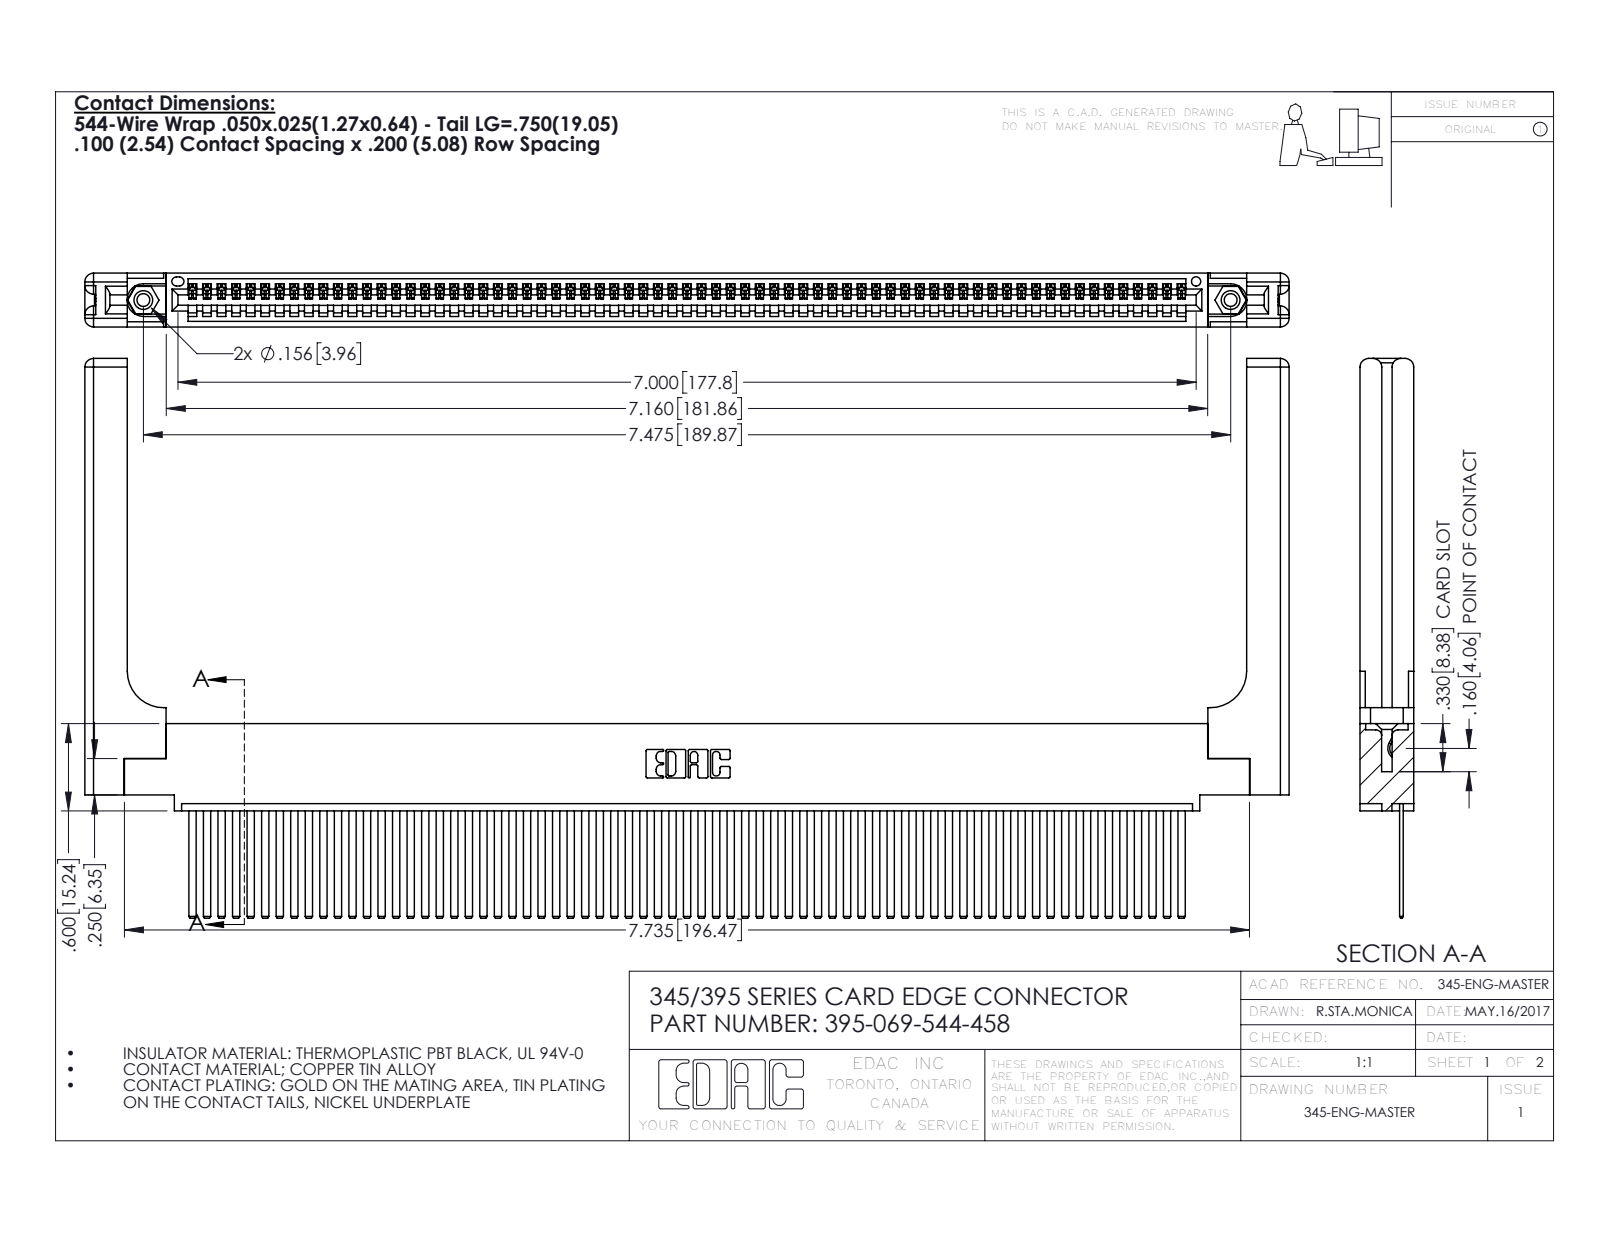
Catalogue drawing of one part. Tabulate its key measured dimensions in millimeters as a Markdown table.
| quantity | value |
| --- | --- |
| part name | 345-220-058_345-220-058; 395-069-544-458; 345-250-001_345-250-001-102; 345-292-001_345-293-144 (+1 more) |
| STEP written by | SolidWorks 2016 (CONFIG_CONTROL_DESIGN) |
| units | millimeters |
| bodies | 74 solids, 3974 faces (2716 planar, 1198 cylindrical, 60 other) |
| overall size | 210.3 × 97.7 × 9.4 |
| volume | 29 430 mm³ |
| surface area | 35 950 mm² |
| round holes (diameter × count) | 2.3 × 2, 3.2 × 2, 4 × 2, 1.6 × 1 |
| round bosses / shafts (diameter × count) | 3.9 × 2 |
| partial cylindrical surfaces (radius × count) | 0.2 × 138, 0.3 × 22, 1.5 × 16, 0.2 × 6, 0.8 × 6, 0.7 × 3, 0.8 × 2, 0.8 × 2 |
| main face-to-face distances | 1.8, 7.6, 2.5, 6.9, 0.6, 9.4, 5.1, 5.7, 3.8, 3.8 |
| hole center spacings | 6.9, 183.9, 189.9 |
